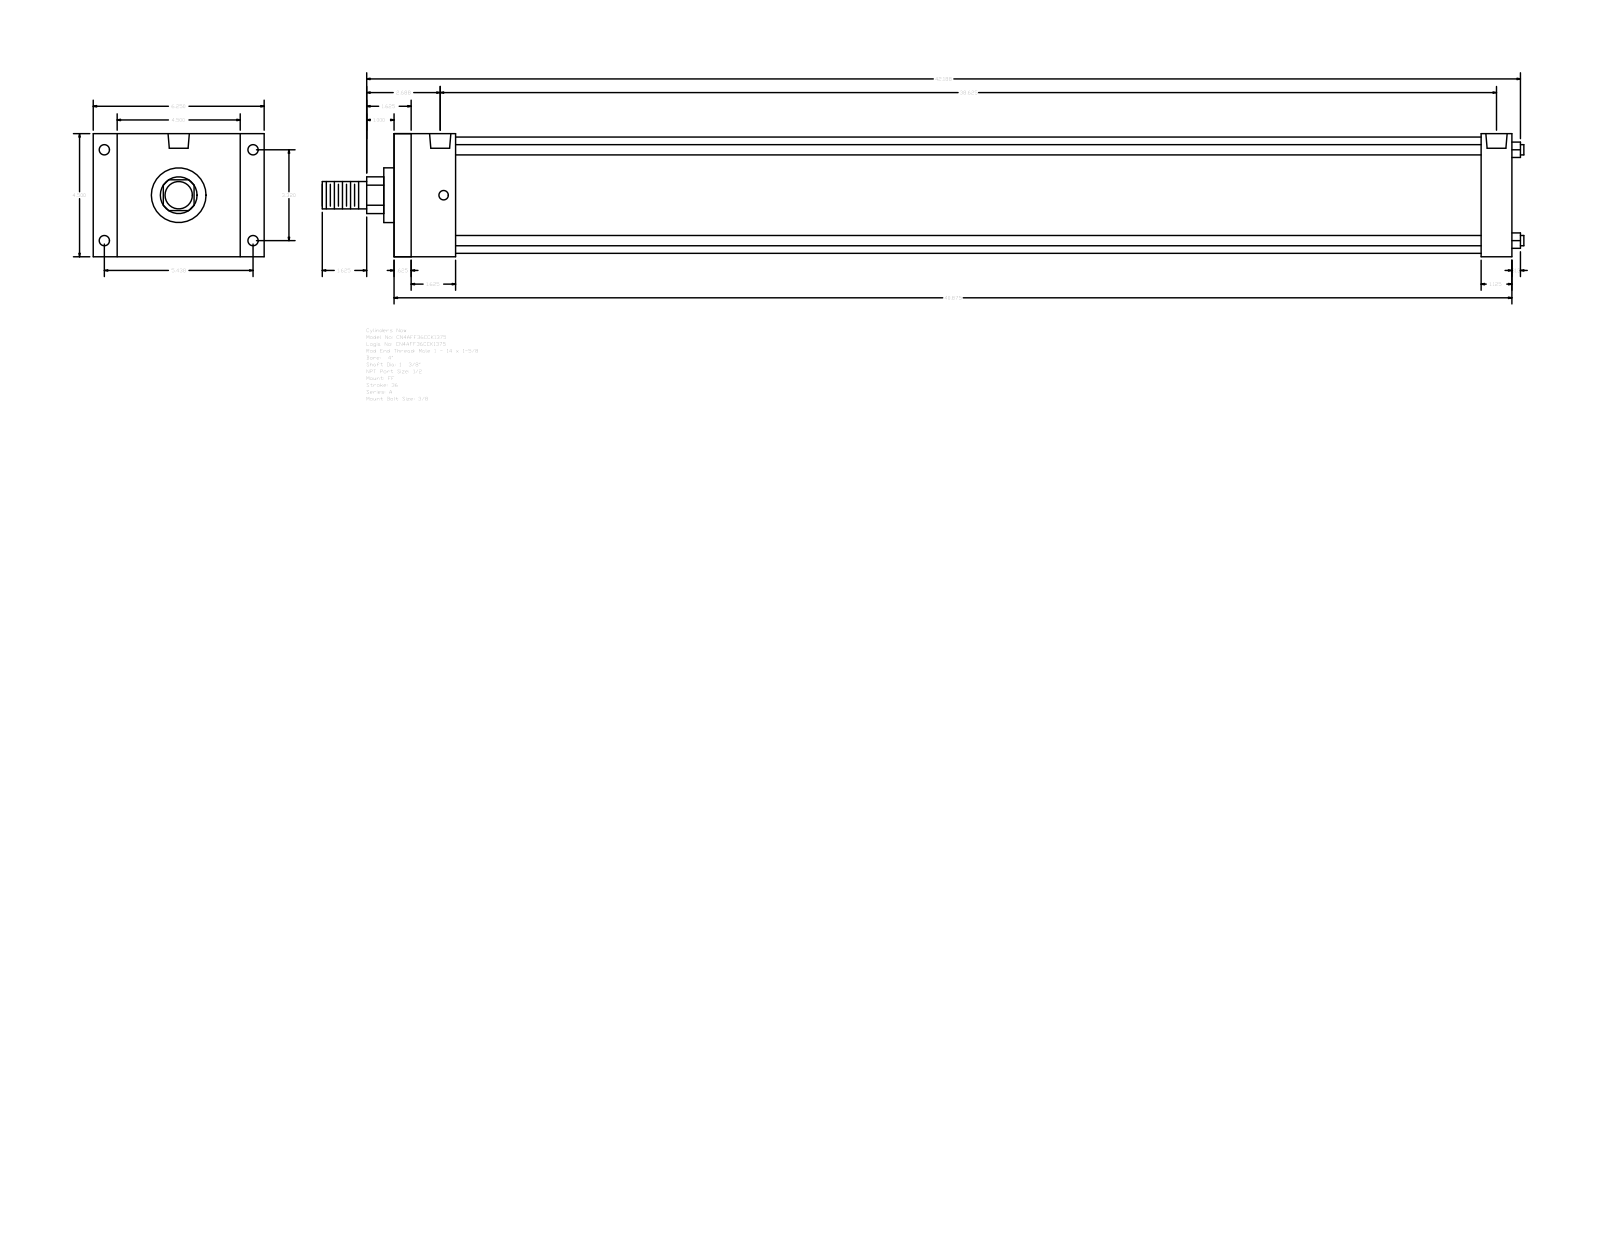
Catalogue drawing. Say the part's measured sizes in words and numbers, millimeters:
The part is named "A_FF__0400_1.375". Its 3-D file was written by "GSSL Pune (CONFIG_CONTROL_DESIGN)". It is 0 solids with 92 faces: 64 planar, 28 cylindrical and 0 other. Overall it measures 1116.01 by 158.75 by 114.3 millimeters. Round holes: 4 of diameter 8.73, 4 of diameter 9.53, 2 of diameter 19.77. Round bosses or shafts: 4 of diameter 9.53, 1 of diameter 107.95, 1 of diameter 50.8, 1 of diameter 34.92, 1 of diameter 25.4. Partial cylindrical surfaces (rounded edges, fillets, slot ends): 1 of radius 17.06. The main face-to-face distances are 114.3, 1038.22, 1022.35, 15.87, 57.15, 28.57, 22.23, 136.53, 1009.65, 993.78. The hole center spacings are 3.18, 84.32, 138.12, 161.82, 974.72, 977.9, 981.08.
